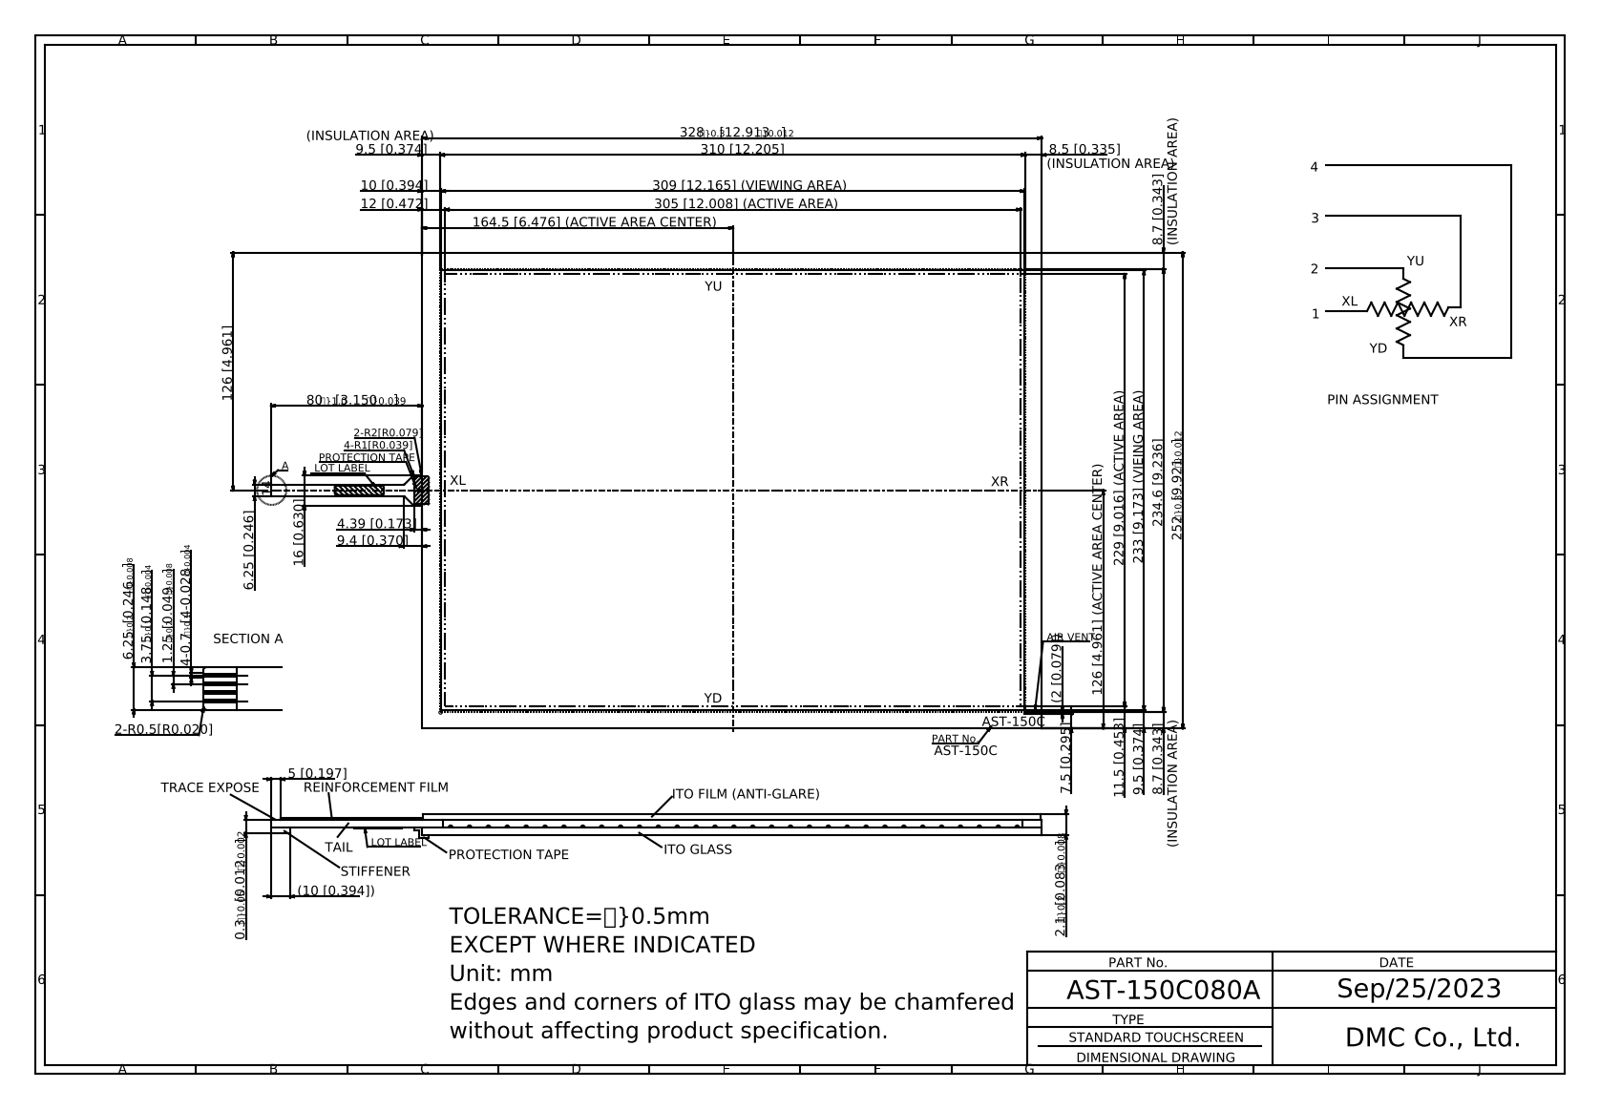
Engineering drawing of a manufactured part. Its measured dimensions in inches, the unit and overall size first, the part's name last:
Units: inches
Overall size (bounding box): 16.063 × 9.921 × 0.083
Partial cylindrical surfaces — rounded edges, fillets, slot ends (radius × count): R0.039 ×4, R0.02 ×2
Main face-to-face distances: 0.083, 0.079, 9.921, 0.075, 12.913, 0.071, 0.059, 0.016, 0.02, 0.024
Volume: 10.58 in³ · Surface area: 262.1 in²
Bodies: 1 solid, 51 faces (45 planar, 6 cylindrical, 0 other)
Part name (STEP PRODUCT): AST-150C080A
STEP written by: Autodesk Inventor 2020 (CONFIG_CONTROL_DESIGN)
